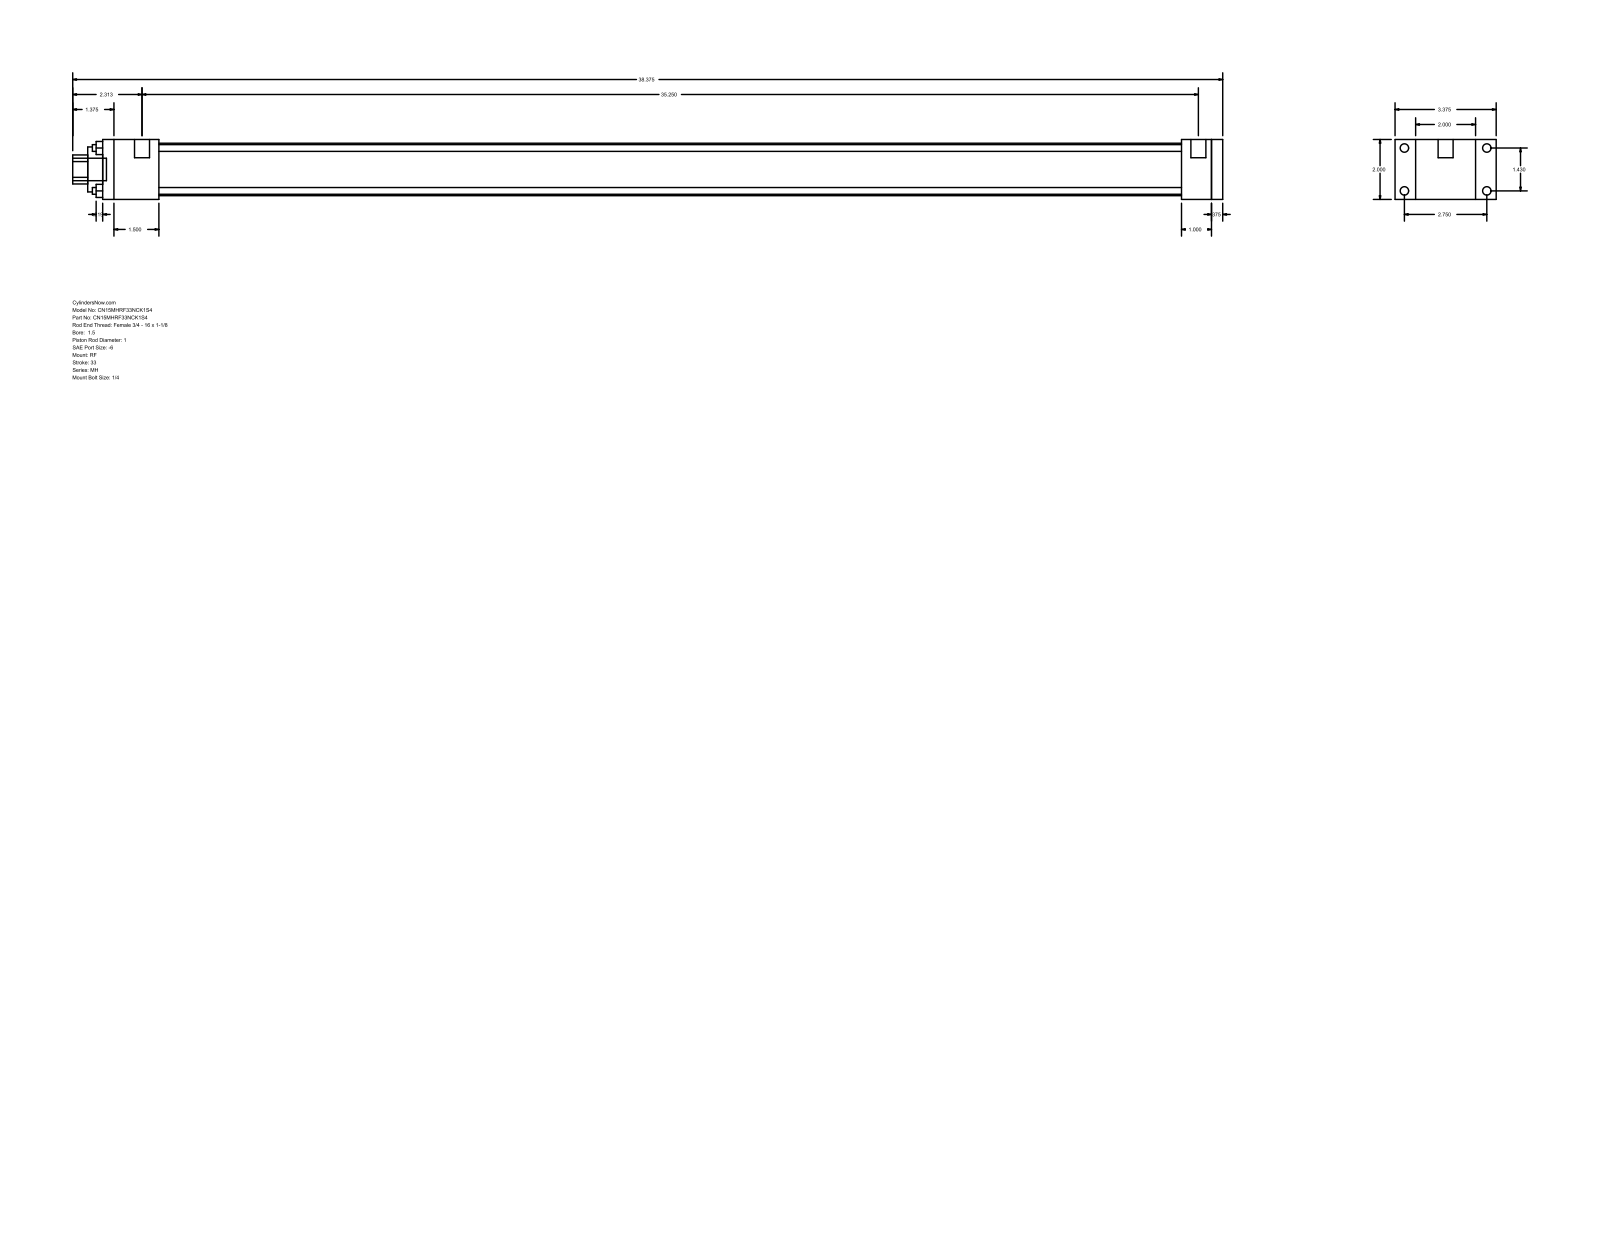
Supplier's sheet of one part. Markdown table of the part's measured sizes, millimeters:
| quantity | value |
| --- | --- |
| part name | MH_RF__0150_1 |
| STEP written by | GSSL Pune (CONFIG_CONTROL_DESIGN) |
| units | millimeters |
| bodies | 0 solids, 92 faces (64 planar, 28 cylindrical, 0 other) |
| overall size | 974.73 × 85.72 × 50.8 |
| round holes (diameter × count) | 5.71 × 4, 25.4 × 1, 38.1 × 1, 44.45 × 1 |
| round bosses / shafts (diameter × count) | 7.14 × 4, 5.56 × 4, 12.7 × 2, 19.05 × 1 |
| partial cylindrical surfaces (radius × count) | 12.29 × 1 |
| main face-to-face distances | 50.8, 9.53, 939.8, 25.4, 949.33, 17.46, 68.26, 914.4, 34.93, 47.63 |
| hole center spacings | 25.68, 36.32, 51.36 |
